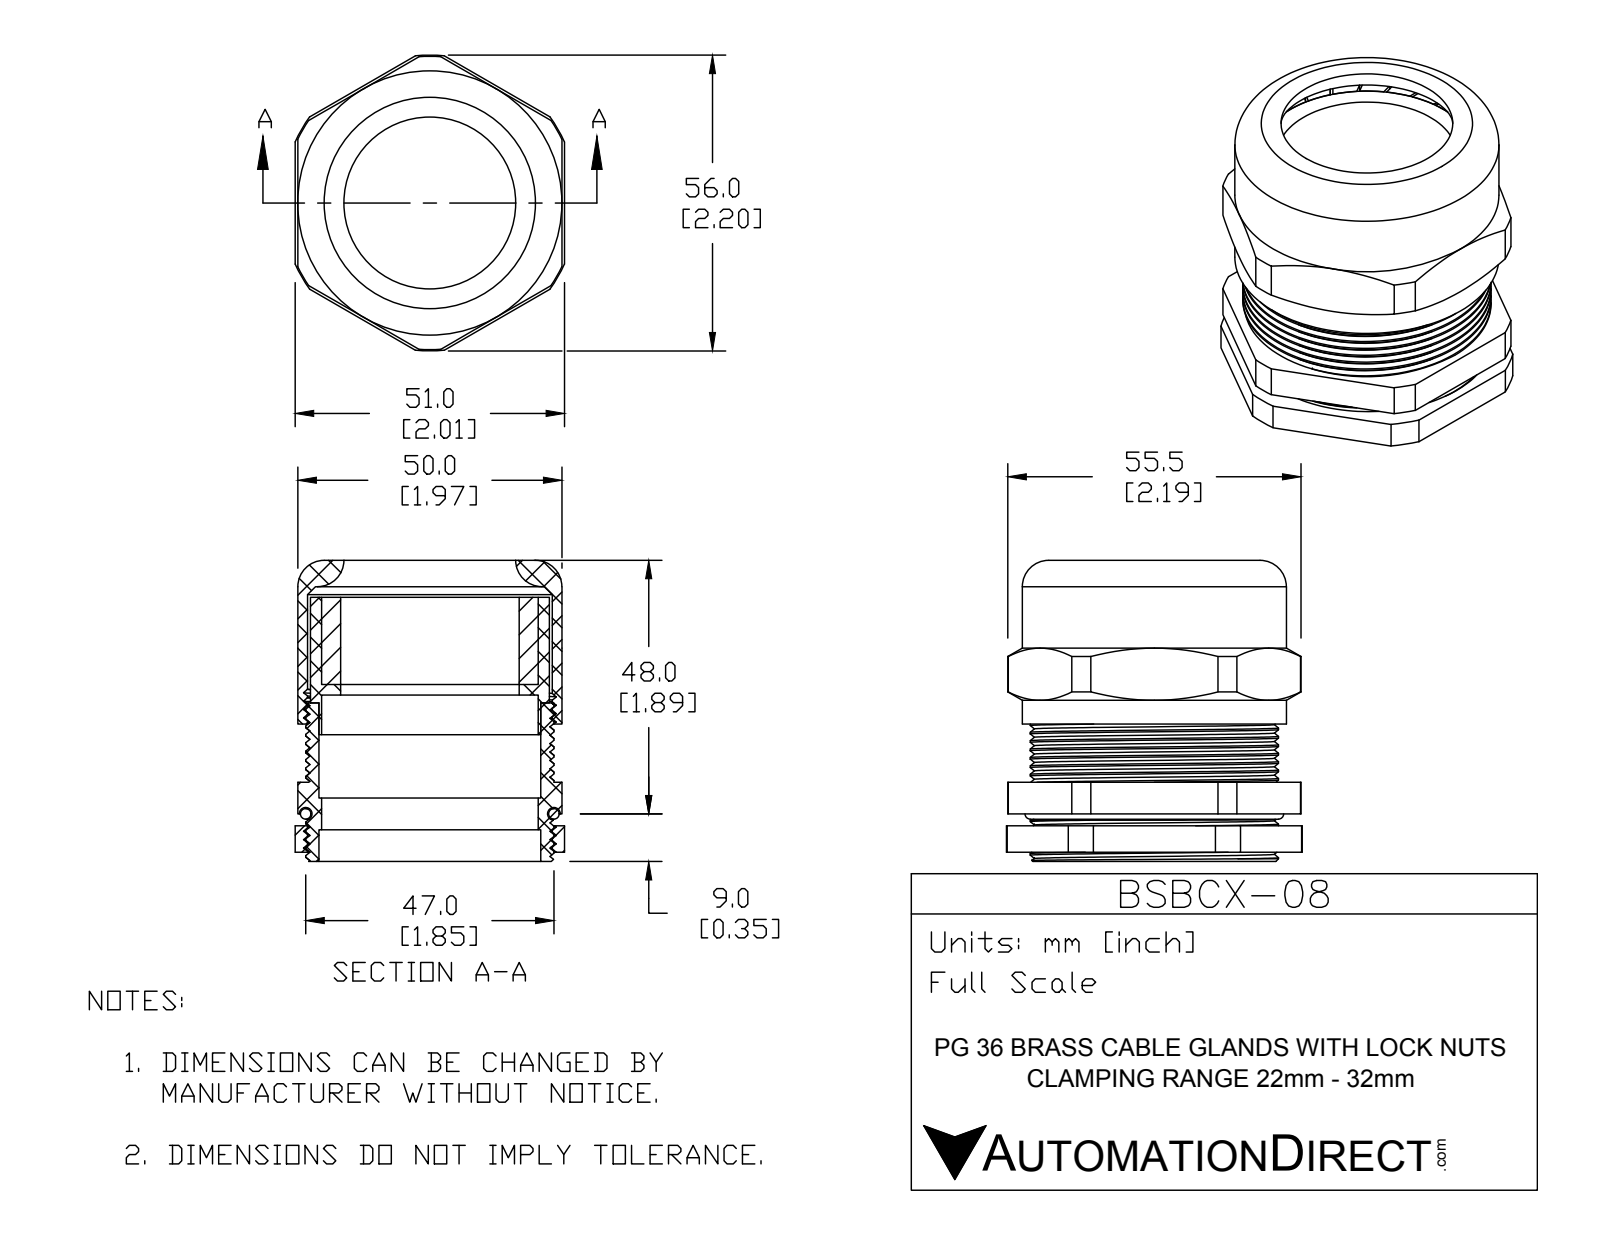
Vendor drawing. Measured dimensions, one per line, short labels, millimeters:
name: BSBCX-08
written by: SolidWorks 2015 (CONFIG_CONTROL_DESIGN)
unit: mm
bodies: 6 solids, 266 faces (137 planar, 91 cylindrical, 38 other)
size: 57 × 56 × 51
volume: 41 326 mm³; area: 41 749 mm²
holes: 1× ⌀33.8, 1× ⌀41, 1× ⌀42, 1× ⌀46.33
bosses: 1× ⌀50, 1× ⌀47, 1× ⌀45.25
rounds: 1× R27.75, 1× R28
face distances: 0.5, 50, 16.5, 18.5, 15, 50.5, 20, 5, 2, 3.5
